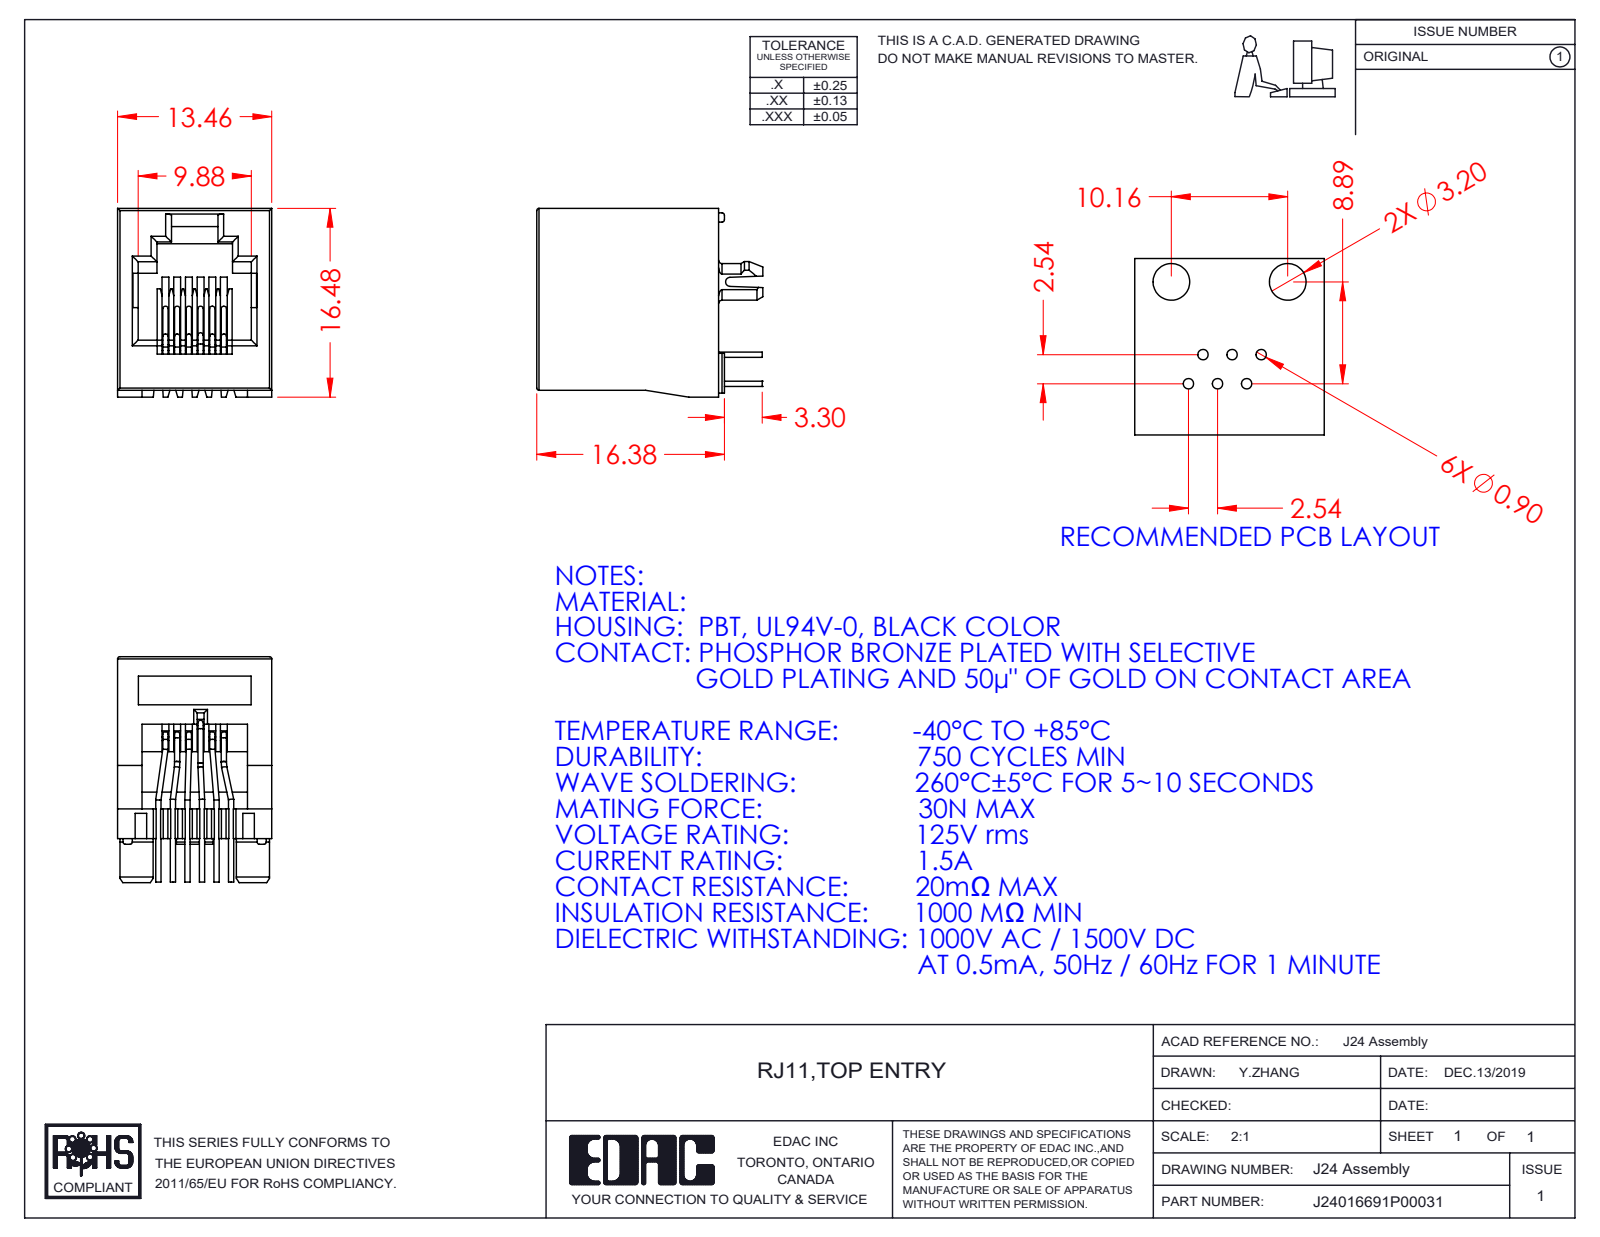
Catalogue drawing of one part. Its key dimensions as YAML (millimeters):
part_name: "RJ24016691P00071; 24 Contacts_MBB; 24 Insulator_MBB"
step_written_by: "SolidWorks 2016 (CONFIG_CONTROL_DESIGN)"
units: millimeters
bodies: {solids: 7, faces: 450, planar: 262, cylindrical: 152, other: 36}
overall_size: [19.73, 16.48, 13.46]
volume: 1746
surface_area: 2940
round_holes:
  - {diameter: 0.46, count: 6}
  - {diameter: 2.1, count: 2}
round_bosses_or_shafts:
  - {diameter: 0.46, count: 27}
partial_cylinders:
  - {radius: 0.5, count: 18}
  - {radius: 0.2, count: 10}
  - {radius: 0.32, count: 6}
  - {radius: 0.34, count: 6}
  - {radius: 0.25, count: 3}
  - {radius: 1.6, count: 2}
  - {radius: 1.77, count: 2}
  - {radius: 0.4, count: 1}
face_to_face_distances: [13.46, 1.02, 1.79, 11.67, 2.04, 0.6, 15.87, 8.24, 3.43, 10.03]
hole_center_spacings: [2.84, 2.54, 4.58, 5.08, 13.1, 6.84, 10.16, 10.35]
